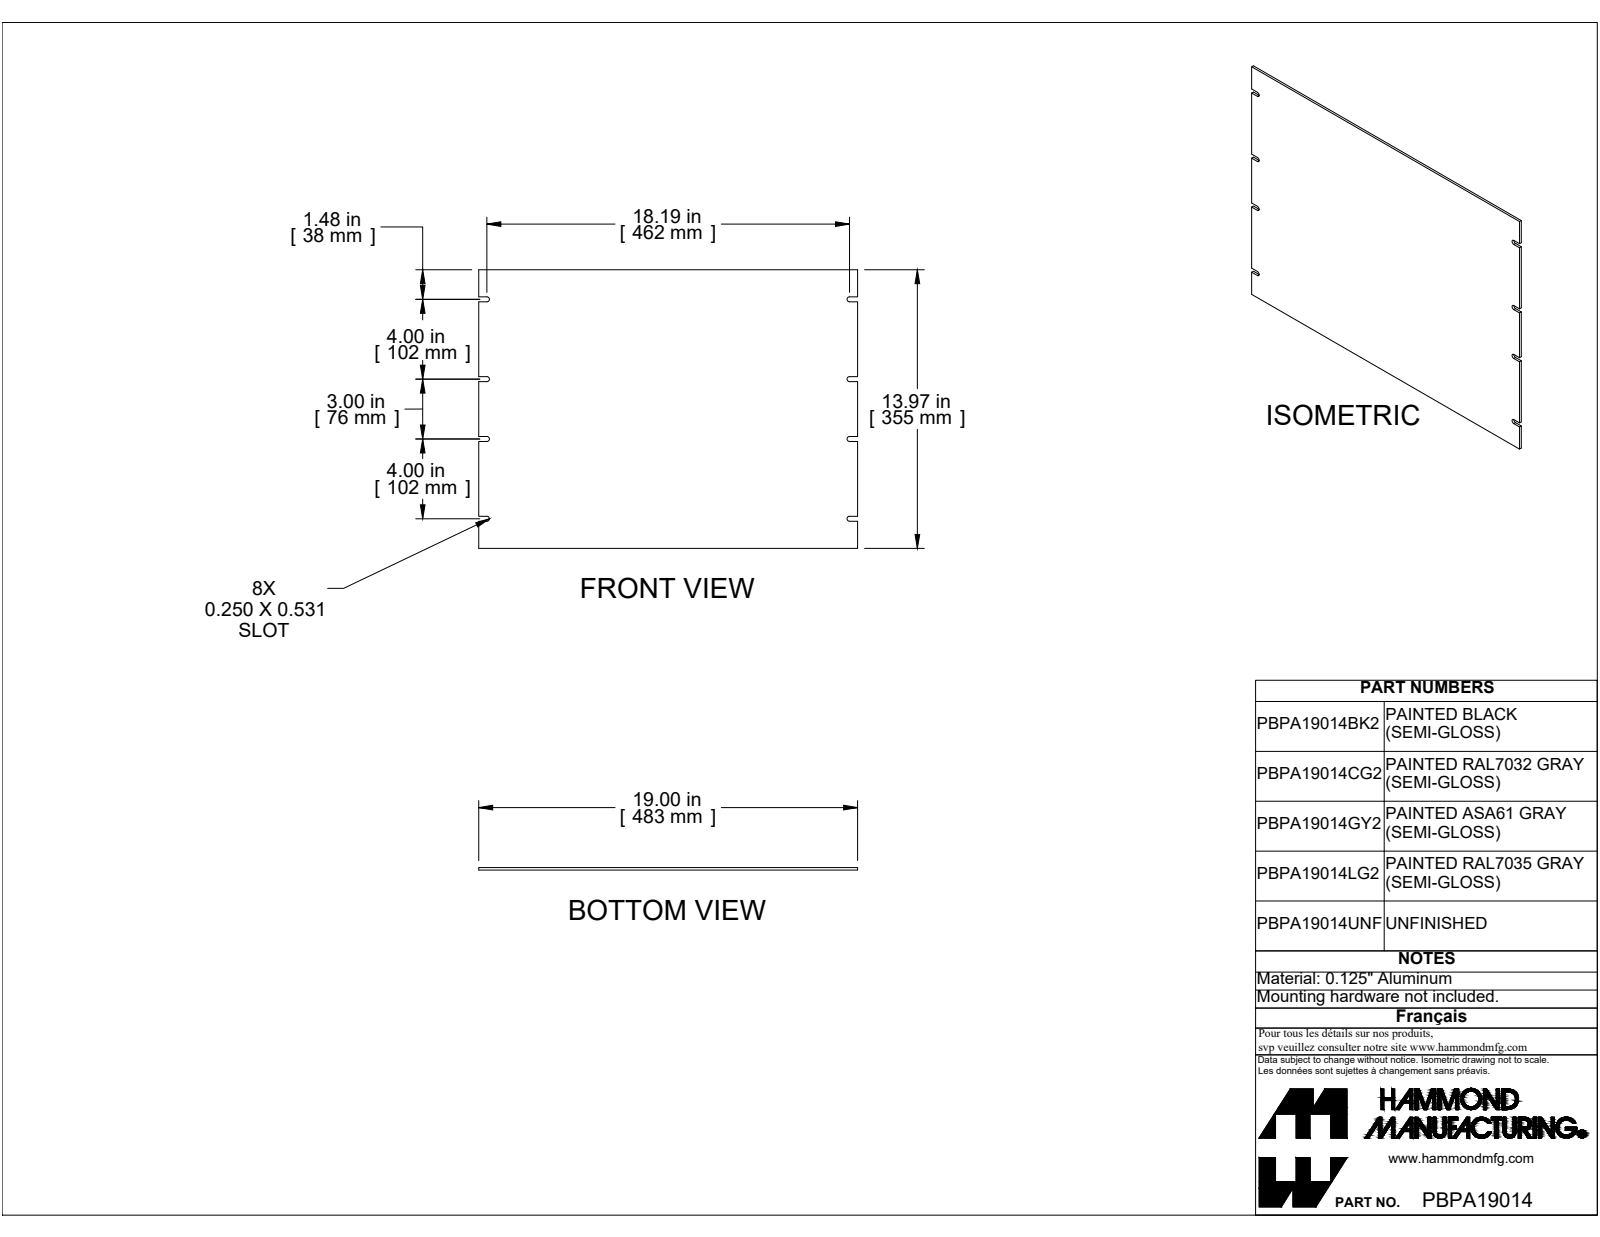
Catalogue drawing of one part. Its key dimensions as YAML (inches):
part_name: "PBPA19014GY2"
step_written_by: "SolidWorks 2019 (CONFIG_CONTROL_DESIGN)"
units: inches
bodies: {solids: 1, faces: 38, planar: 30, cylindrical: 8, other: 0}
overall_size: [19, 13.968, 0.125]
volume: 33.05
surface_area: 538
partial_cylinders:
  - {radius: 0.125, count: 8}
face_to_face_distances: [0.125, 13.968, 19, 7, 0.25, 4, 1.609, 5.359, 8.609, 12.359]
